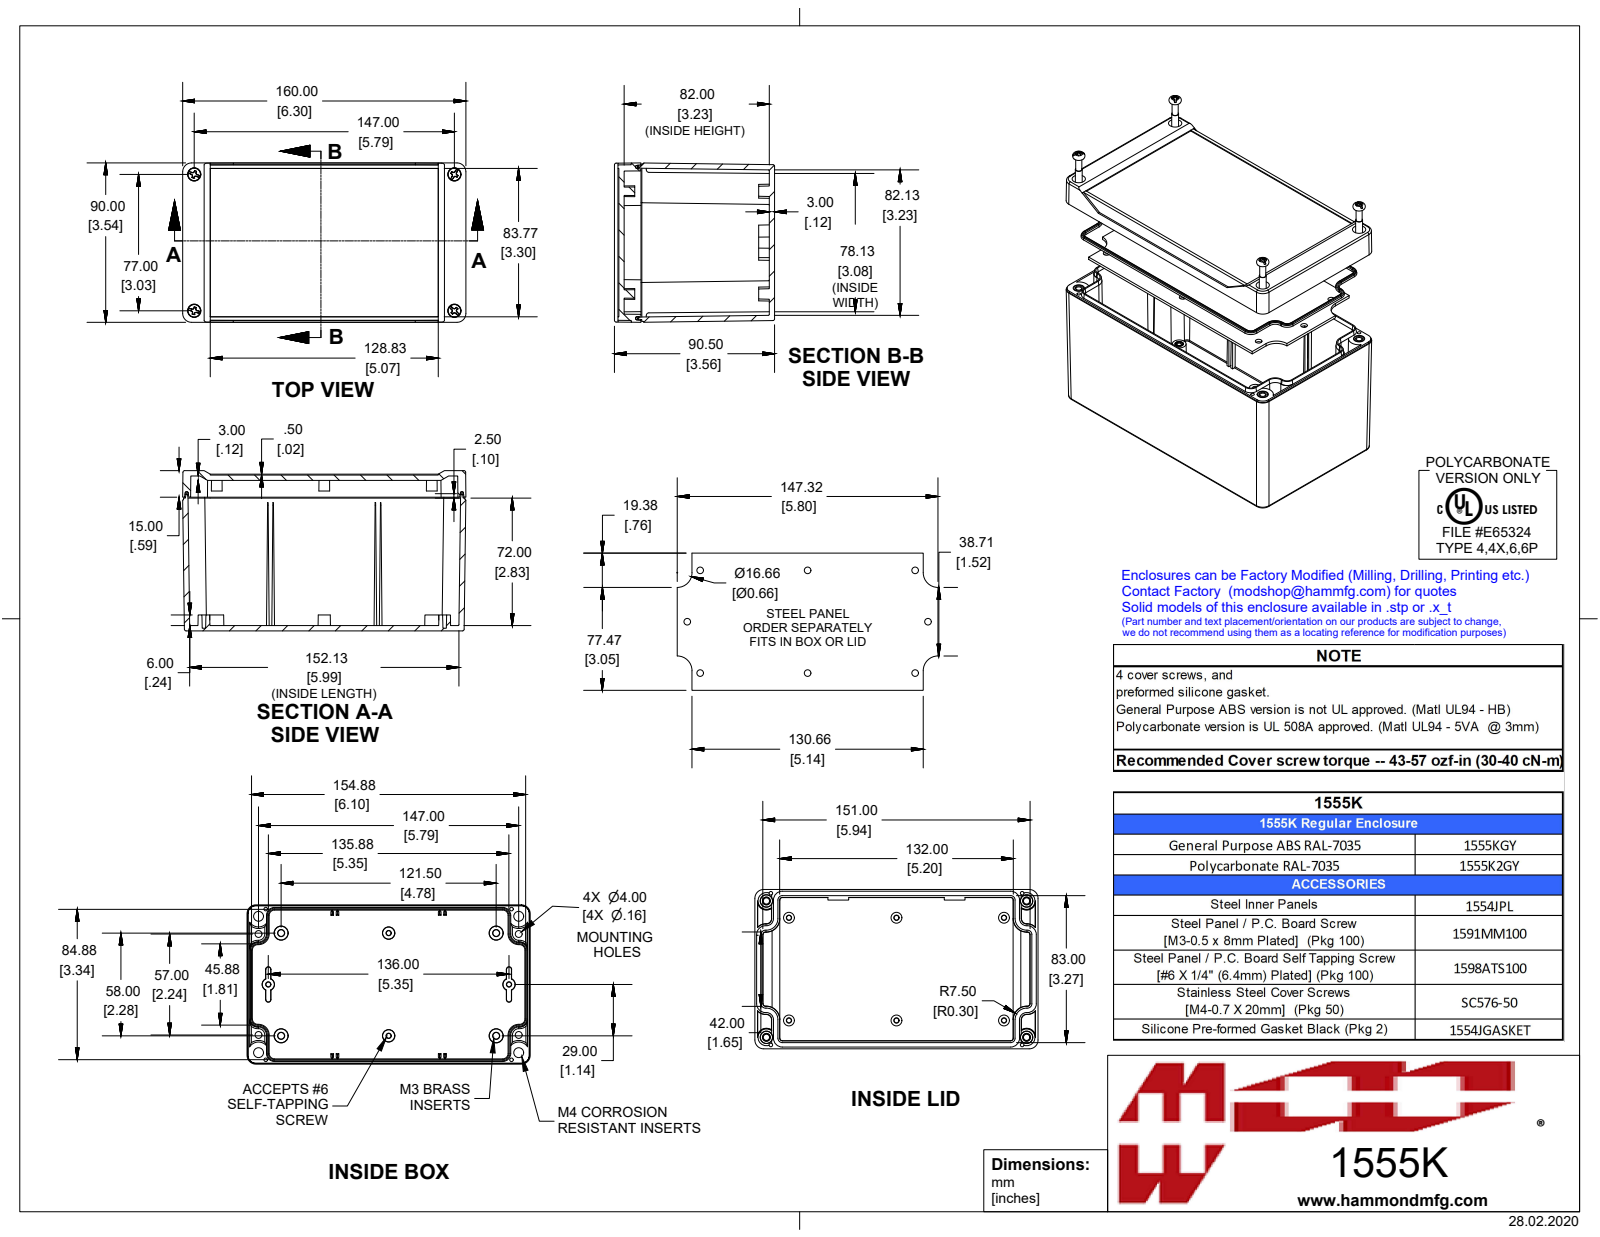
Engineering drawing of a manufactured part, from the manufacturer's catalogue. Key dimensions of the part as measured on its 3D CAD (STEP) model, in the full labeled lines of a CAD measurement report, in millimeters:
Part name (STEP PRODUCT): 1555K2GY
STEP written by: SolidWorks 2019 (AUTOMOTIVE_DESIGN)
Units: millimetres
Bodies: 16 solids, 1388 faces (418 planar, 336 cylindrical, 634 other)
Overall size (bounding box): 160 × 90.5 × 90
Volume: 255 600 mm³ · Surface area: 195 300 mm²
Round holes (diameter × count): ⌀2 ×8, ⌀2.5 ×4, ⌀2.8 ×4, ⌀3.3 ×4, ⌀3.5 ×4, ⌀3.7 ×4, ⌀7 ×4
Round bosses / shafts (diameter × count): ⌀6.4 ×4, ⌀5.5 ×4, ⌀5.3 ×4, ⌀4.8 ×4, ⌀3.9 ×4, ⌀3.9 ×4, ⌀3.8 ×4, ⌀3.4 ×4
Partial cylindrical surfaces — rounded edges, fillets, slot ends (radius × count): R0.5 ×24, R1 ×8, R5 ×8, R4.7 ×4, R8.3 ×4, R1.5 ×2
Main face-to-face distances: 3, 85, 9, 6, 79, 88, 10.6, 7.6, 1.6, 77.4
Hole centre spacings: 16.1, 72.6, 150.3, 15.9, 17.2, 29.9, 58, 72.1
